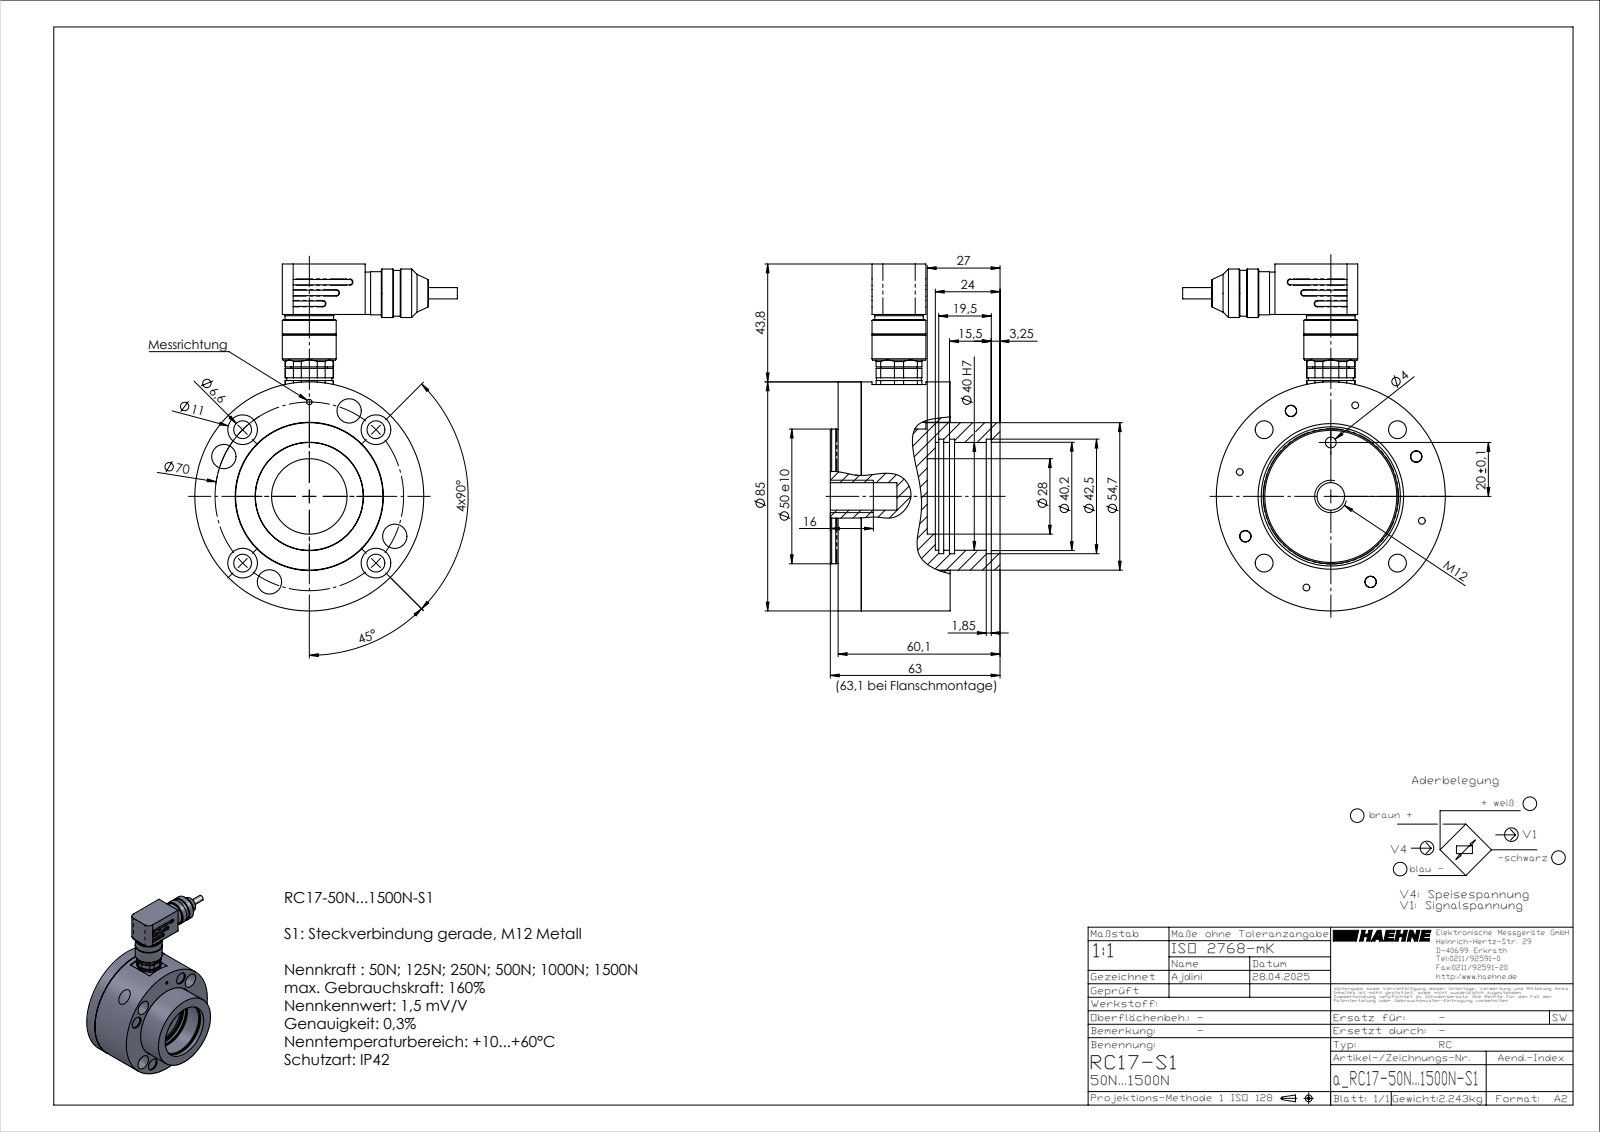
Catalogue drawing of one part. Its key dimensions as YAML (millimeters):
part_name: "a_RC17-50N...1500N-S1; a_RC-N2 Flanschmontage Scheibe; a_RC17-50N...1500N-S1 STEP"
step_written_by: "SolidWorks 2023 (AUTOMOTIVE_DESIGN)"
units: millimeters
bodies: {solids: 16, faces: 540, planar: 267, cylindrical: 180, other: 93}
overall_size: [128.75, 97.48, 63.1]
volume: 265727
surface_area: 81561
round_holes:
  - {diameter: 2.5, count: 4}
  - {diameter: 3.4, count: 4}
  - {diameter: 4.2, count: 4}
  - {diameter: 5.3, count: 4}
  - {diameter: 6.6, count: 4}
  - {diameter: 9, count: 4}
  - {diameter: 11, count: 4}
  - {diameter: 2, count: 1}
  - {diameter: 4, count: 1}
  - {diameter: 4.5, count: 1}
  - {diameter: 6, count: 1}
  - {diameter: 8.37, count: 1}
round_bosses_or_shafts:
  - {diameter: 8.5, count: 4}
  - {diameter: 5.7, count: 4}
  - {diameter: 5, count: 4}
  - {diameter: 3, count: 4}
  - {diameter: 1.5, count: 4}
  - {diameter: 1, count: 4}
  - {diameter: 18, count: 2}
  - {diameter: 16, count: 2}
partial_cylinders:
  - {radius: 0.2, count: 12}
  - {radius: 1, count: 11}
  - {radius: 0.3, count: 6}
  - {radius: 4, count: 2}
  - {radius: 0.57, count: 1}
  - {radius: 0.65, count: 1}
  - {radius: 0.77, count: 1}
  - {radius: 3.5, count: 1}
face_to_face_distances: [8.6, 3, 11.6, 33, 44.6, 41.6, 11.5, 2, 44.5, 2.9]
hole_center_spacings: [35, 49.5, 12.16, 18.12, 23.94, 29.58, 40.15, 57.34]
